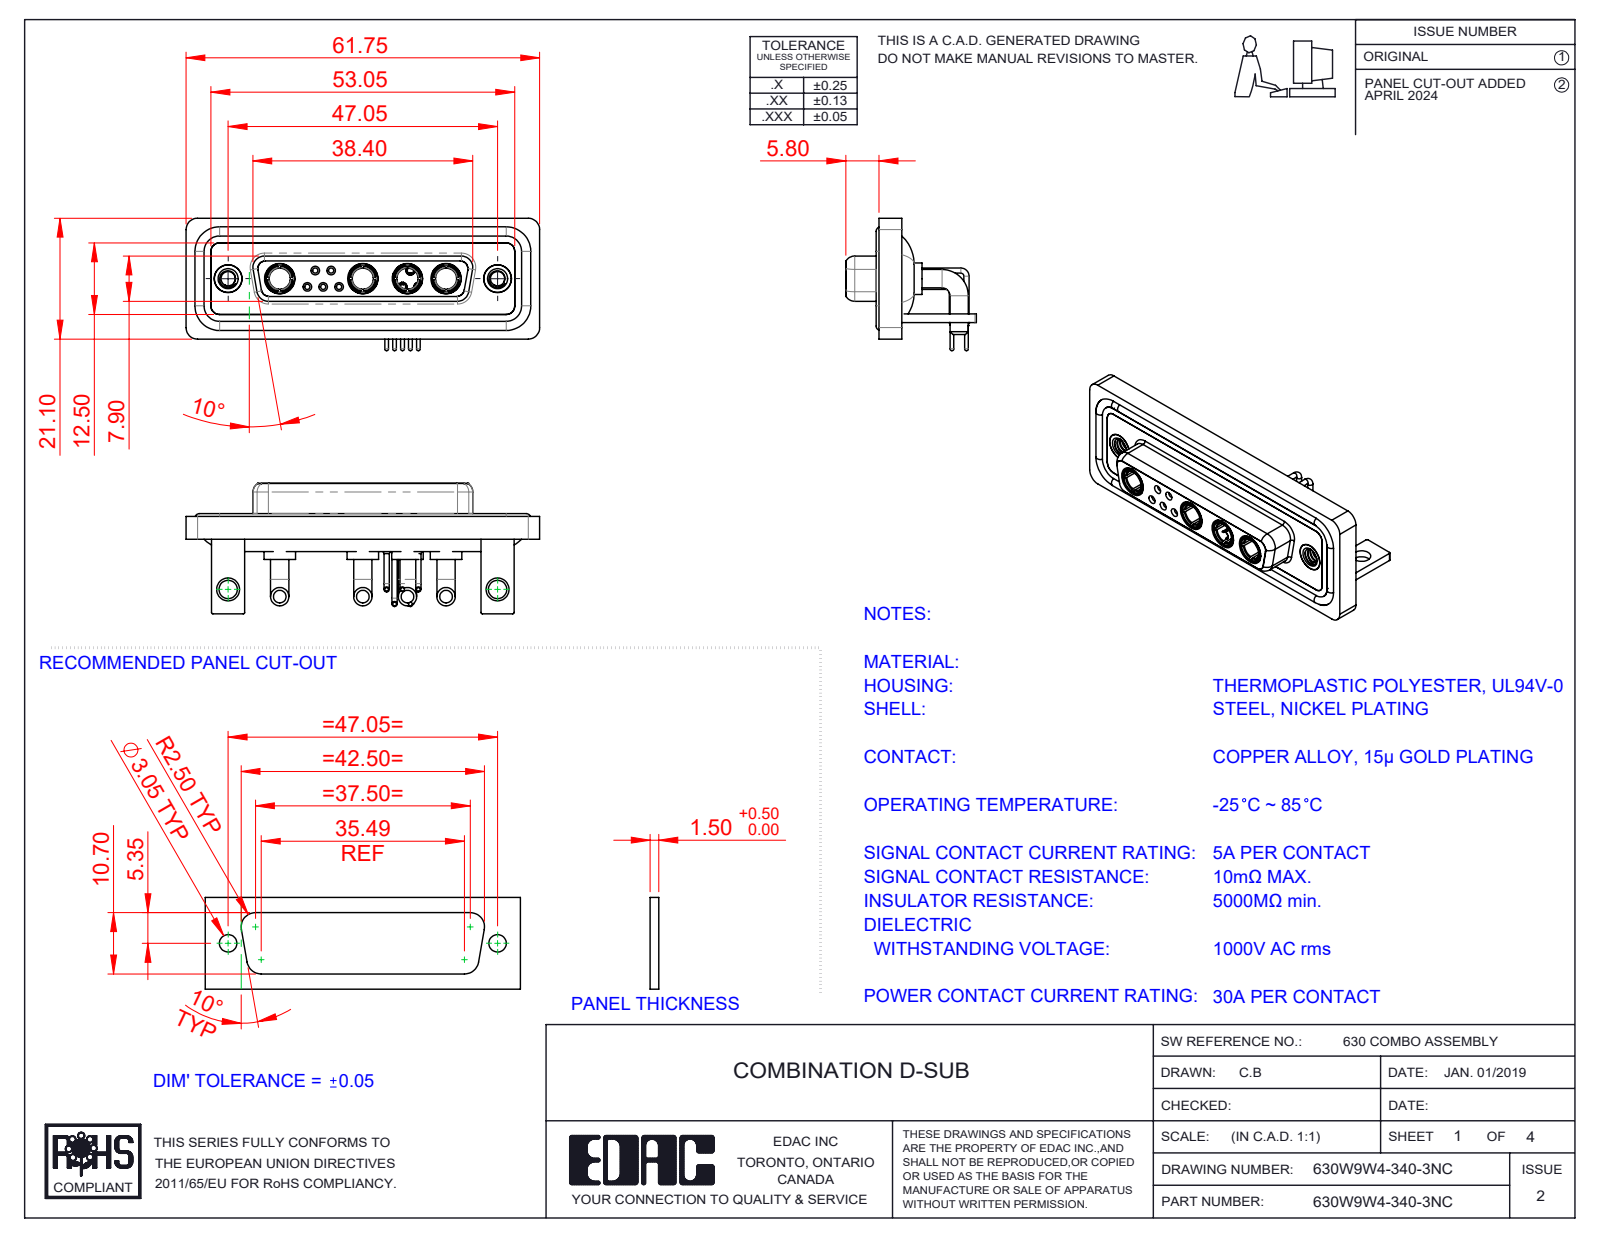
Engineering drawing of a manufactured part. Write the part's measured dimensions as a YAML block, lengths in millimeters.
part_name: "630Combo Housing_9W4; 630Combo Contact Row 1_50 Contacts; 630Combo Shell Front_25 Contacts; 630Combo Contact Row 2_50 Contacts (+6 more)"
step_written_by: "SolidWorks 2023 (CONFIG_CONTROL_DESIGN)"
units: millimeters
bodies: {solids: 22, faces: 1005, planar: 316, cylindrical: 425, other: 264}
overall_size: [61.75, 23.12, 22.8]
volume: 8923
surface_area: 14859
round_holes:
  - {diameter: 4.85, count: 6}
  - {diameter: 0.9, count: 5}
  - {diameter: 1.1, count: 5}
  - {diameter: 1.5, count: 5}
  - {diameter: 2, count: 5}
  - {diameter: 3.7, count: 4}
  - {diameter: 5.3, count: 4}
  - {diameter: 1.6, count: 3}
  - {diameter: 1.7, count: 2}
  - {diameter: 2.5, count: 2}
  - {diameter: 3.2, count: 2}
  - {diameter: 4, count: 2}
round_bosses_or_shafts:
  - {diameter: 0.9, count: 10}
  - {diameter: 1.6, count: 9}
  - {diameter: 3.2, count: 8}
  - {diameter: 2, count: 5}
  - {diameter: 1.5, count: 5}
  - {diameter: 0.65, count: 5}
  - {diameter: 5.5, count: 4}
  - {diameter: 5.2, count: 4}
partial_cylinders:
  - {radius: 2, count: 19}
  - {radius: 1.5, count: 18}
  - {radius: 0.25, count: 16}
  - {radius: 1.35, count: 8}
  - {radius: 1.6, count: 8}
  - {radius: 0.5, count: 5}
  - {radius: 0.6, count: 4}
  - {radius: 0.65, count: 4}
face_to_face_distances: [0.4, 1.8, 2.9, 3.7, 1.5, 4.1, 1.1, 1.4, 1.6, 2.5]
hole_center_spacings: [3.16, 2.77, 5.04, 13.85, 11.08, 12.79, 15.5, 5.54]
